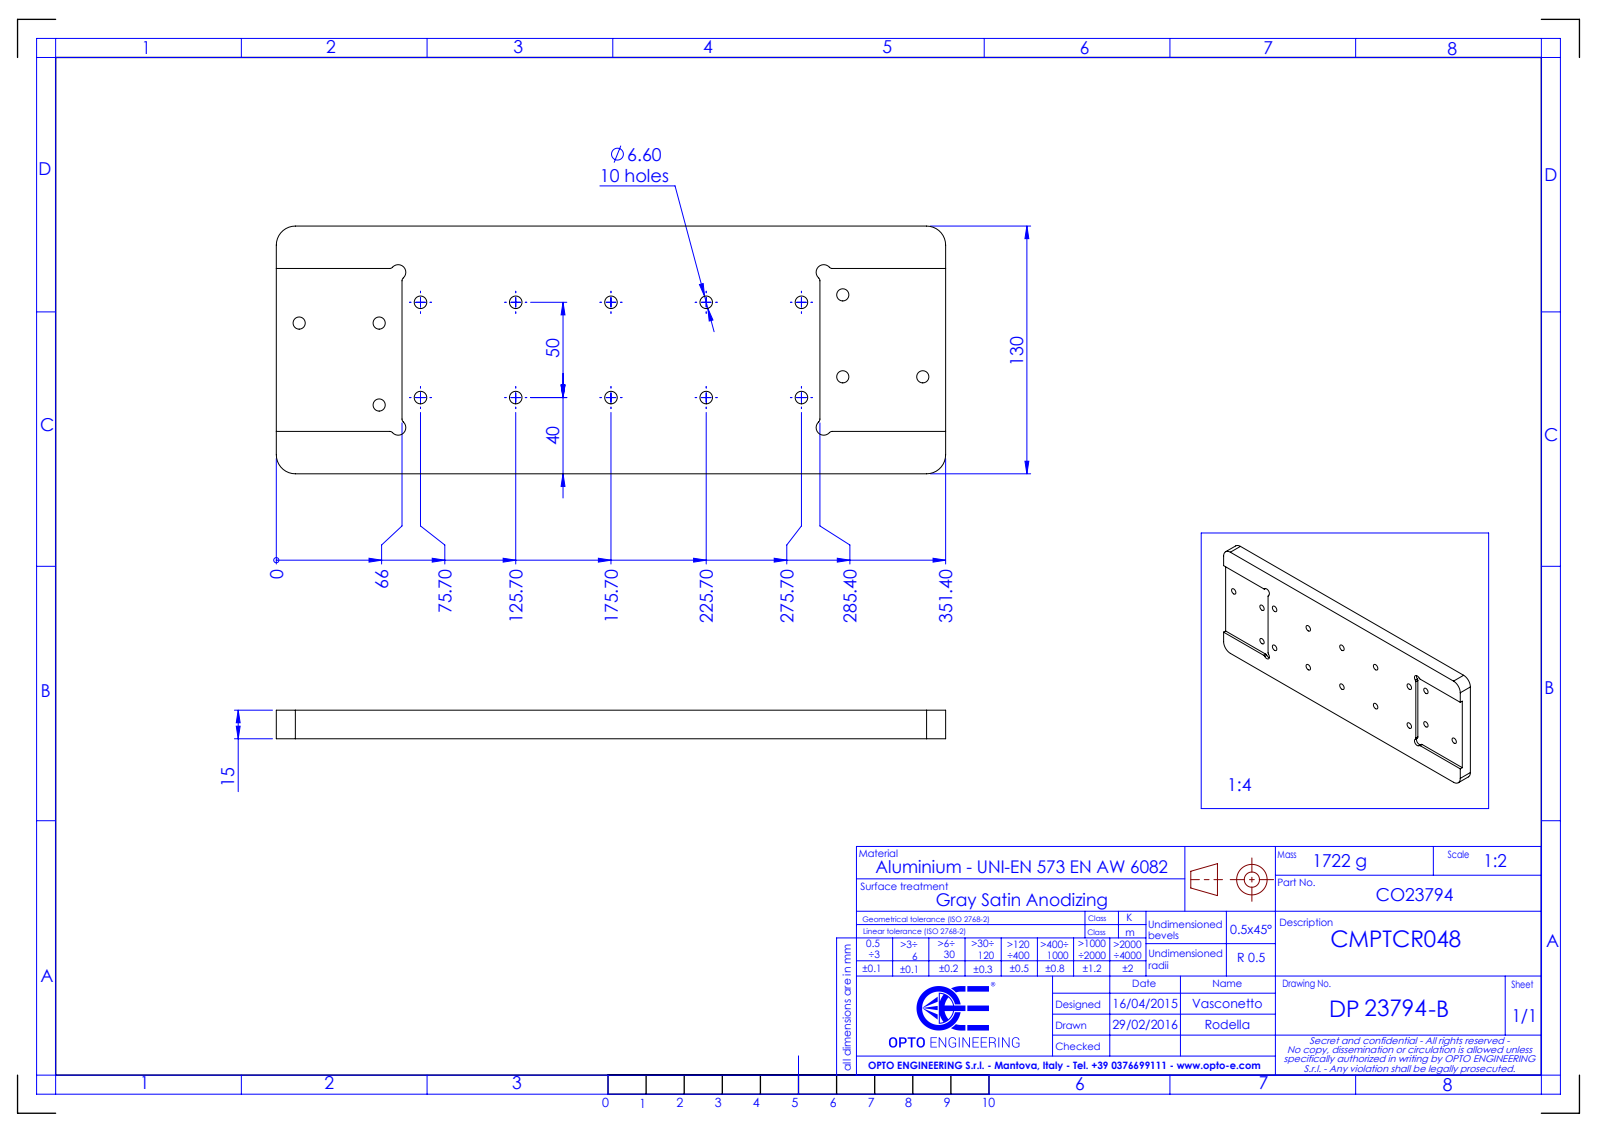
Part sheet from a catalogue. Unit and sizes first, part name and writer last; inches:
Units: inches
Overall size (bounding box): 13.835 × 5.118 × 0.591
Round holes (diameter × count): ⌀0.26 ×10, ⌀0.252 ×6, ⌀0.433 ×6
Partial cylindrical surfaces — rounded edges, fillets, slot ends (radius × count): R0.079 ×8, R0.157 ×4, R0.394 ×4
Main face-to-face distances: 0.591, 0.118, 0.472, 5.118, 13.835, 0.876, 4.242, 2.598, 11.236, 0.339
Hole centre spacings: 1.969, 2.784, 3.937, 4.402, 5.906, 6.225, 0.868, 0.956
Volume: 39.06 in³ · Surface area: 170.9 in²
Bodies: 1 solid, 82 faces (20 planar, 62 cylindrical, 0 other)
Part name (STEP PRODUCT): DP23794
STEP written by: SolidWorks 2021 (CONFIG_CONTROL_DESIGN)
